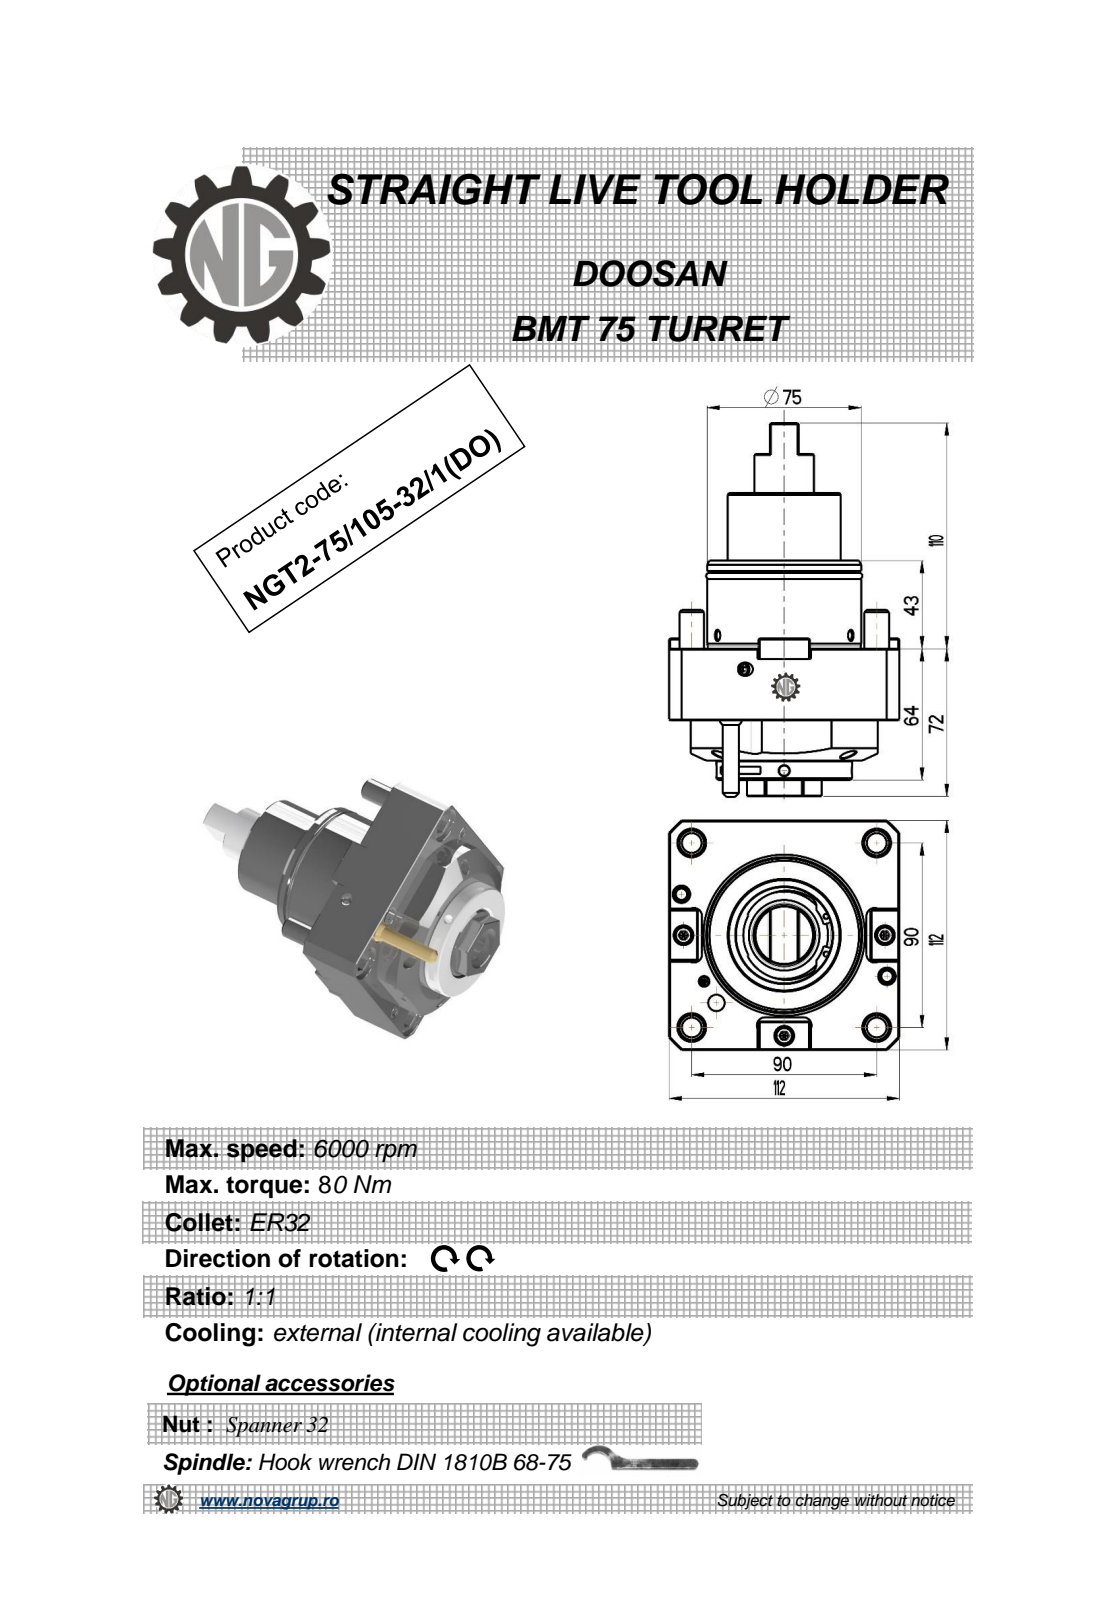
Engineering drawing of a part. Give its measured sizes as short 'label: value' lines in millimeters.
name: NGT2_75_105_32_1_DO
written by: PRO/ENGINEER BY PARAMETRIC TECHNOLOGY CORPORATION, 2010280 (CONFIG_CONTROL_DESIGN)
unit: mm
bodies: 2 solids, 182 faces (75 planar, 51 cylindrical, 56 other)
size: 182.34 × 112 × 112
volume: 902 802 mm³; area: 77 725 mm²
holes: 3× ⌀5, 1× ⌀3, 1× ⌀8, 1× ⌀23, 1× ⌀34
bosses: 4× ⌀12, 1× ⌀75, 1× ⌀70, 1× ⌀66, 1× ⌀55, 1× ⌀29, 1× ⌀8
rounds: 2× R0.8, 1× R6, 1× R51, 1× R75
face distances: 112, 35, 29, 10.5, 101.5, 54.5, 19.5, 64, 76, 9.5
hole spacings: 17.01, 46.67, 55.03
